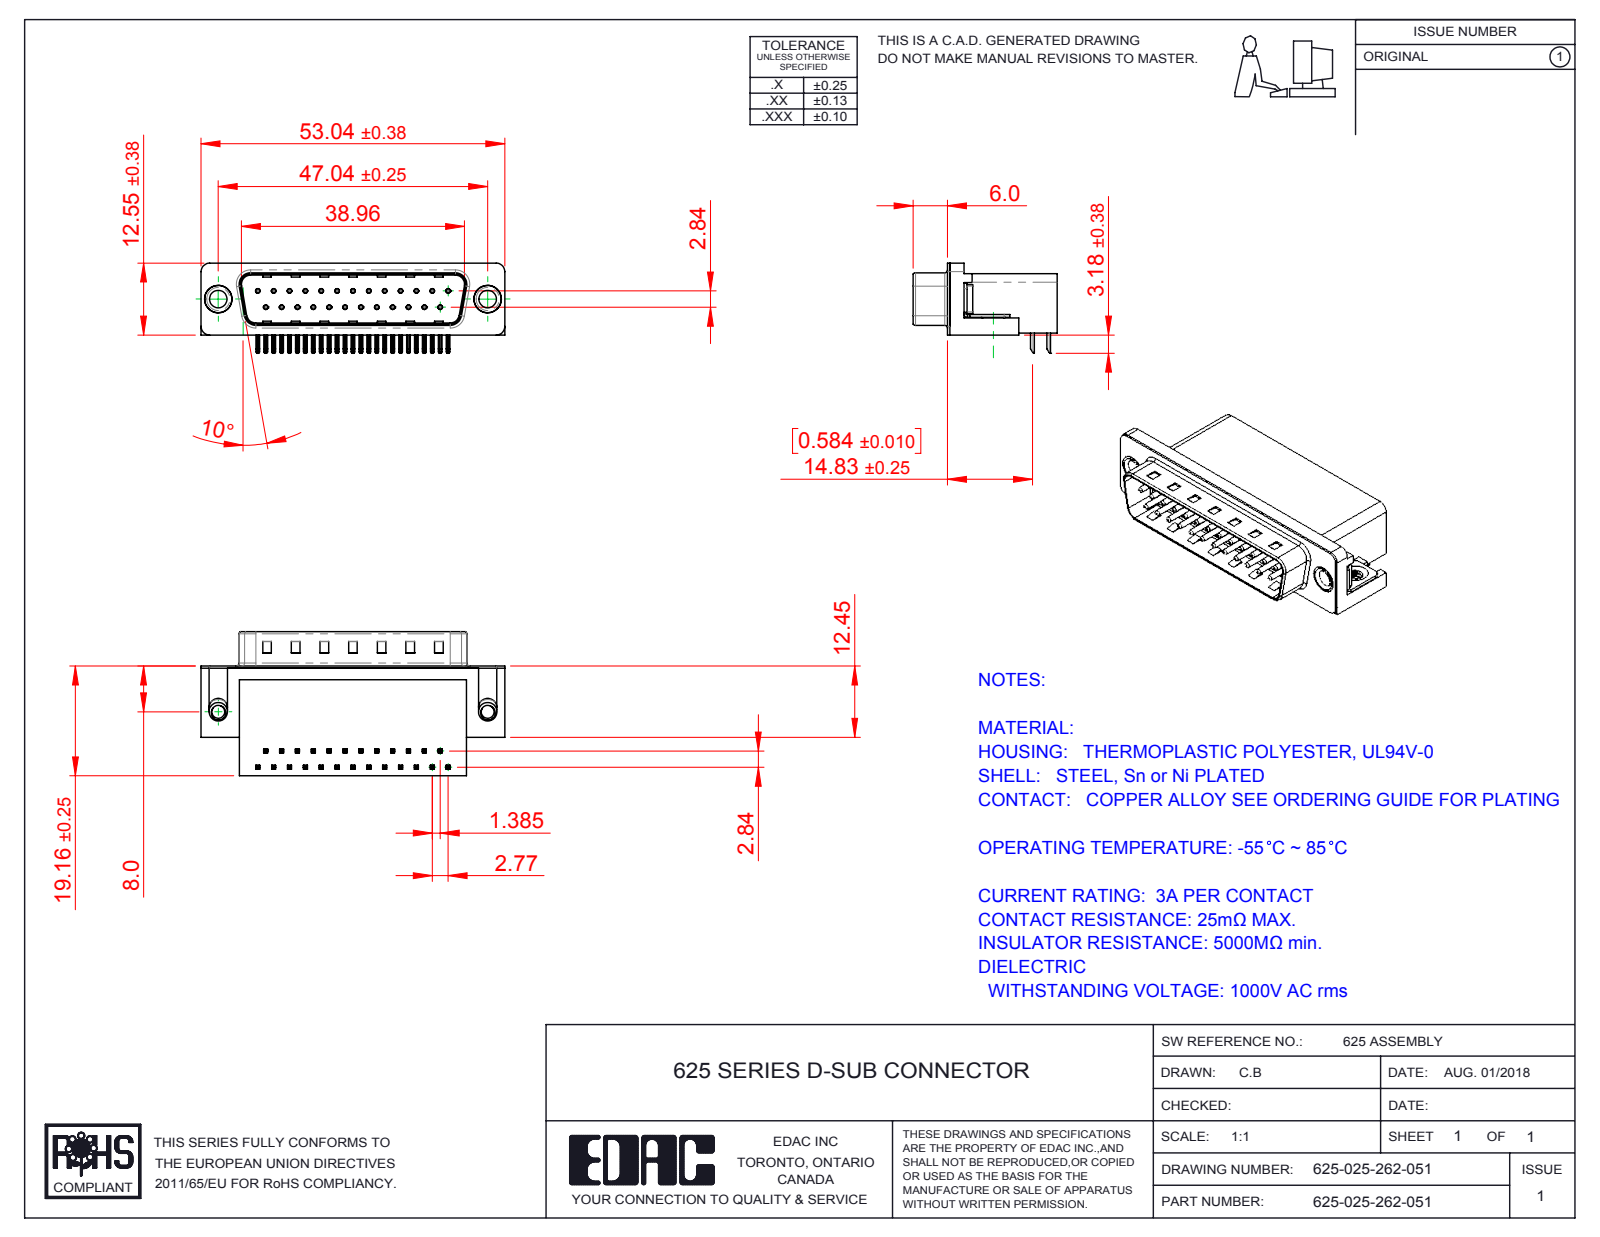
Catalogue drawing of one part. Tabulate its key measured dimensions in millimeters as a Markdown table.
| quantity | value |
| --- | --- |
| part name | 625 Contact Top; 625-025-262-051; 625 Housing_25 Socket; 625 Shell_25 Socket (+3 more) |
| STEP written by | SolidWorks 2016 (CONFIG_CONTROL_DESIGN) |
| units | millimeters |
| bodies | 31 solids, 2257 faces (1407 planar, 655 cylindrical, 195 other) |
| overall size | 53.04 × 25.16 × 15.73 |
| volume | 9 163 mm³ |
| surface area | 8 918 mm² |
| round holes (diameter × count) | 0.35 × 25, 0.8 × 25, 2.26 × 2, 3.05 × 2, 4 × 2, 4.8 × 2, 5 × 2 |
| round bosses / shafts (diameter × count) | 0.75 × 25, 4.9 × 2, 4.75 × 2, 3.85 × 2, 3.26 × 2 |
| partial cylindrical surfaces (radius × count) | 0.25 × 108, 0.12 × 50, 1 × 16, 0.5 × 9, 1.6 × 8, 1.5 × 7, 0.9 × 4, 2 × 4 |
| main face-to-face distances | 0.4, 10.35, 18.76, 2.1, 8.76, 10.46, 10.86, 1.7, 19.16, 10.11 |
| hole center spacings | 3.16, 2.77, 11.08, 5.54, 8.31, 5.03, 13.85, 7.48 |
